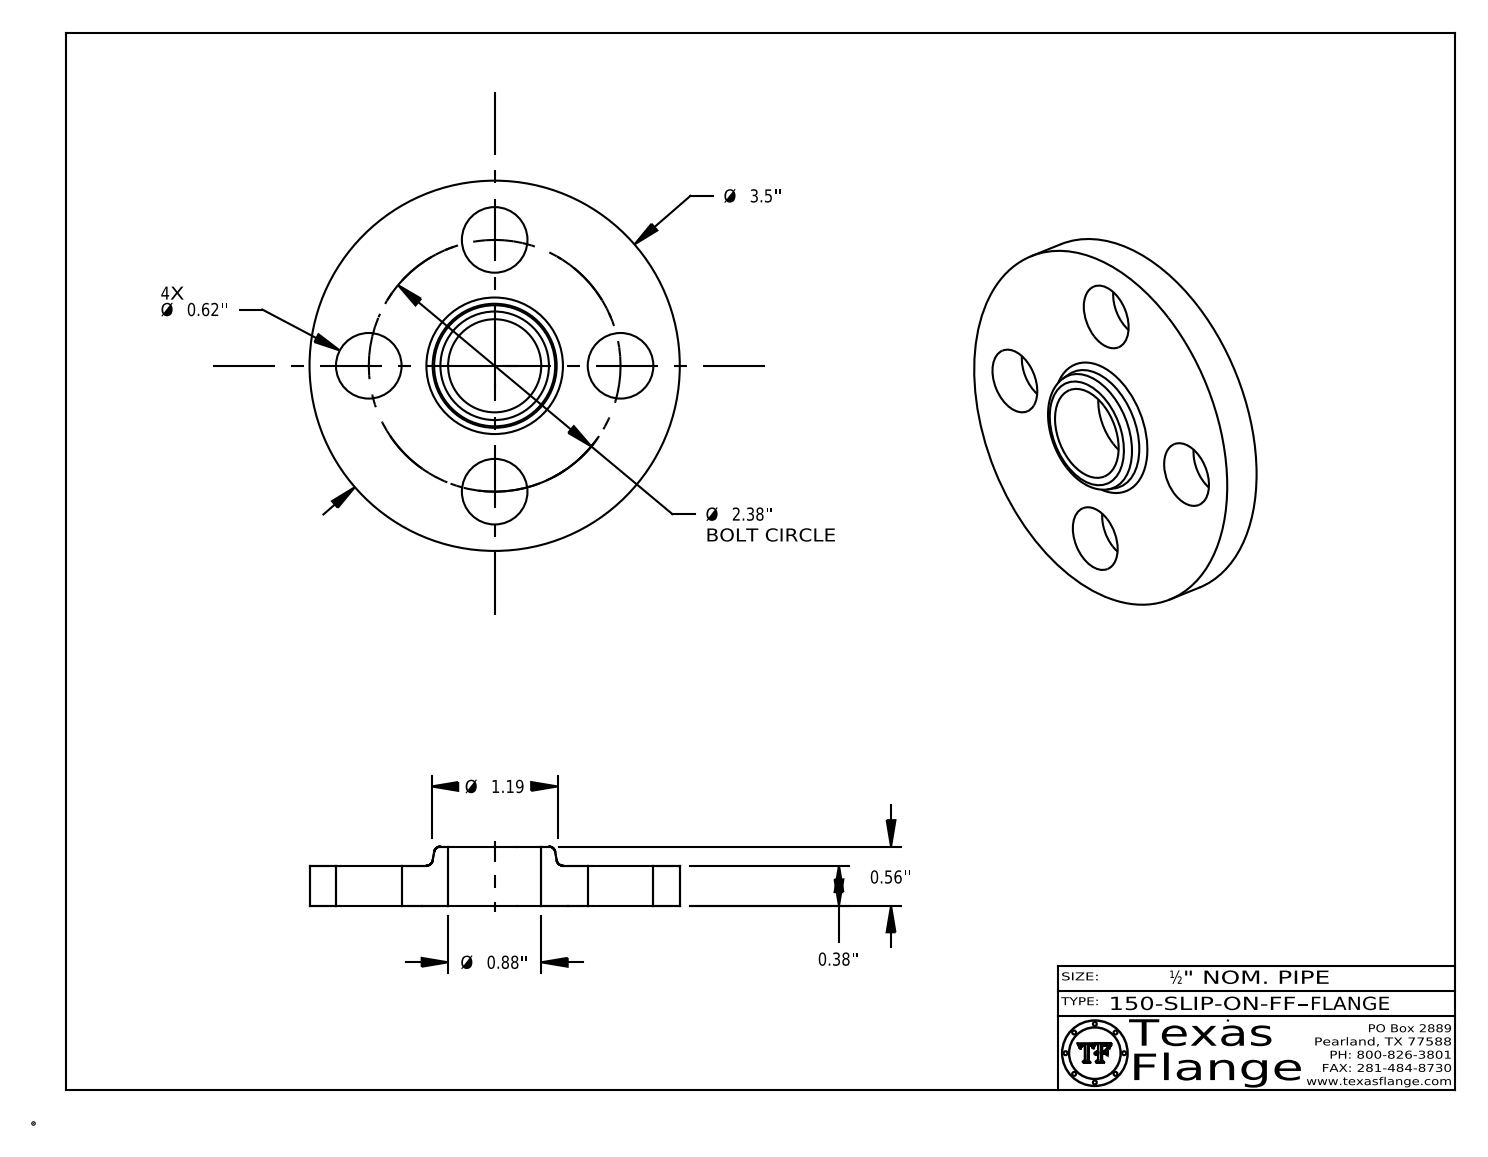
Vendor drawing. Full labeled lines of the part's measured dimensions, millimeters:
Part name (STEP PRODUCT): 150-SLIP-ON-FF
STEP written by: CATIA V5 STEP AP214 (AUTOMOTIVE_DESIGN)
Units: millimetres
Bodies: 1 solid, 407 faces (369 planar, 32 cylindrical, 6 other)
Overall size (bounding box): 88.9 × 88.9 × 14.2
Volume: 49 900 mm³ · Surface area: 16 010 mm²
Round holes (diameter × count): ⌀15.7 ×4, ⌀12.6 ×1, ⌀22.4 ×1
Round bosses / shafts (diameter × count): ⌀0.8 ×8, ⌀88.9 ×1, ⌀9.9 ×1
Main face-to-face distances: 9.7, 14.2, 4.6, 9.3, 0.4, 5, 3.8, 3.7, 0.7, 3.1
Hole centre spacings: 30.2, 42.7, 23.1, 55.9, 60.5, 30.2
